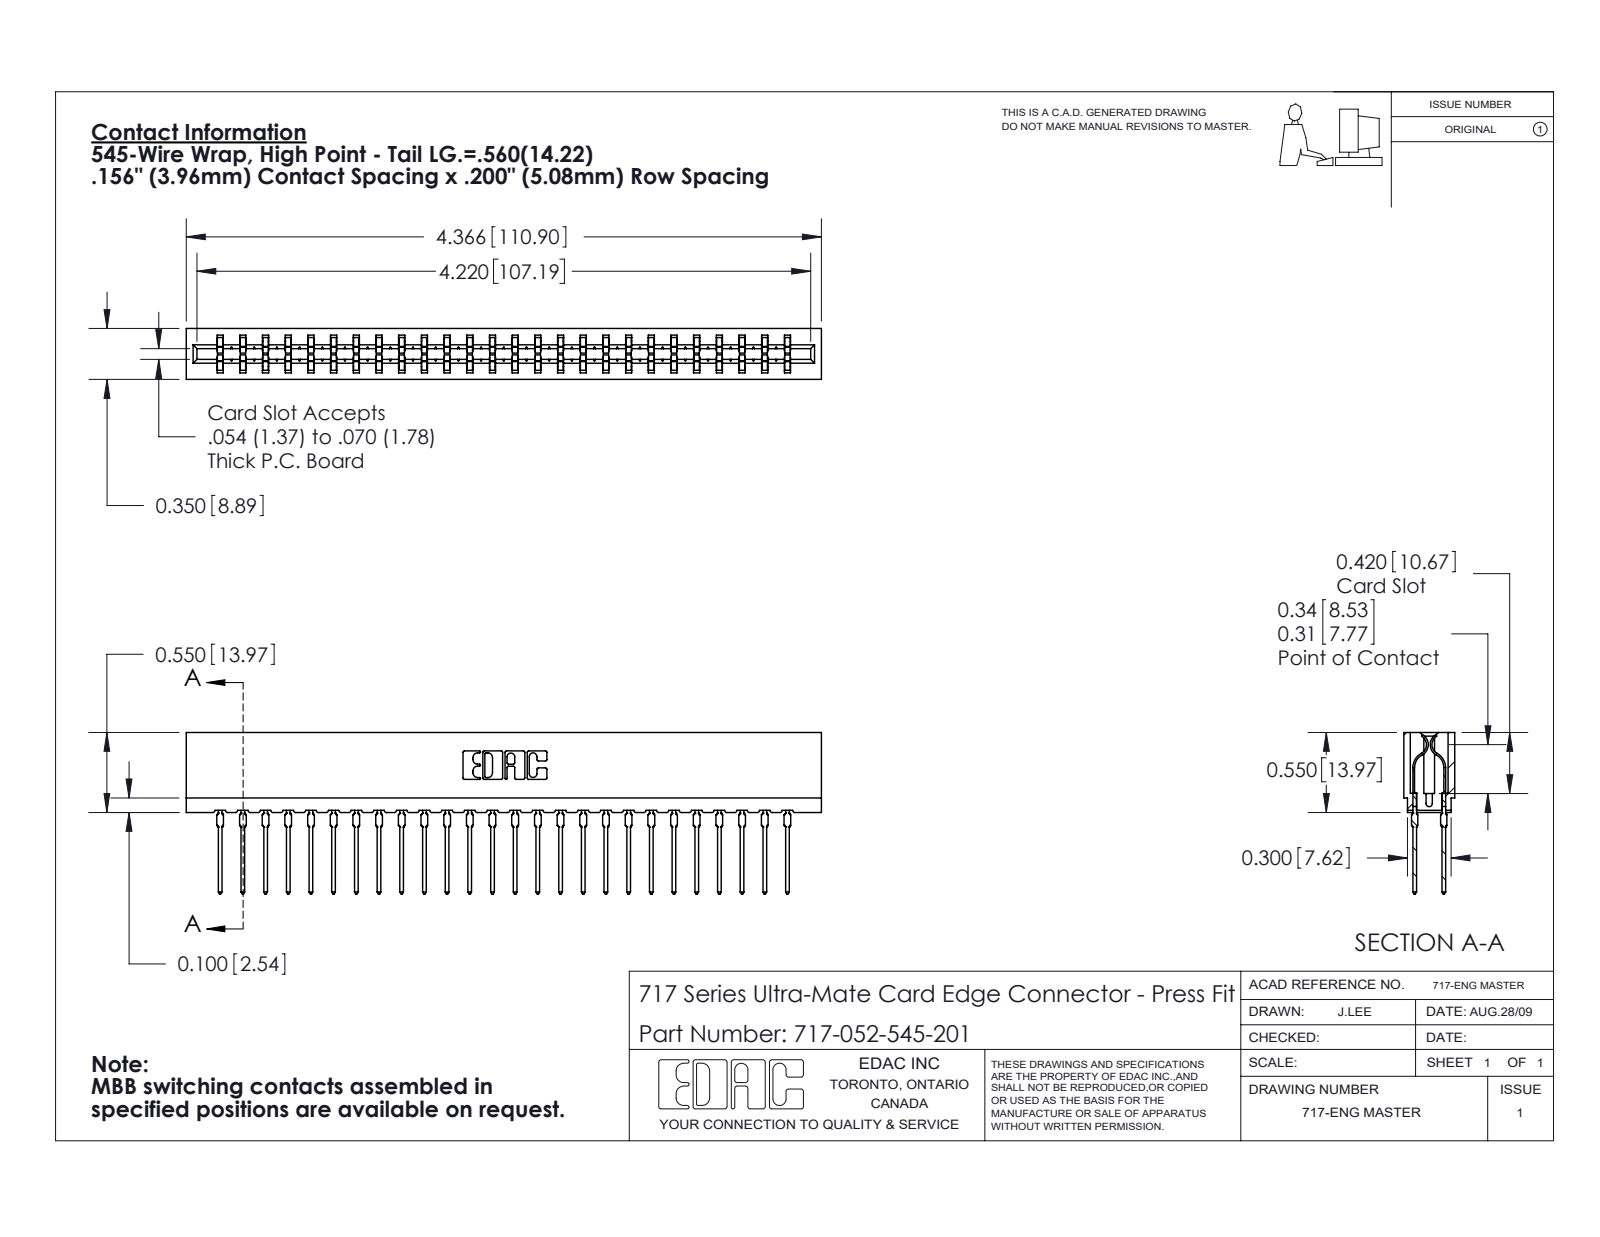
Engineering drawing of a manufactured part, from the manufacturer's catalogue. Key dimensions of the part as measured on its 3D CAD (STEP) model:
Part name (STEP PRODUCT): 717-052-545-201; 745-292-001_545; 717 Part_Insulator Option - 06
STEP written by: SolidWorks 2020 (CONFIG_CONTROL_DESIGN)
Units: inches
Bodies: 53 solids, 4774 faces (2472 planar, 950 cylindrical, 1352 other)
Overall size (bounding box): 4.366 × 1.109 × 0.35
Volume: 0.602 in³ · Surface area: 24.41 in²
Partial cylindrical surfaces — rounded edges, fillets, slot ends (radius × count): R0.021 ×104, R0.015 ×52, R0.01 ×22, R0.005 ×8, R0.011 ×8, R0.007 ×6, R0.031 ×6, R0.026 ×3
Main face-to-face distances: 0.212, 0.138, 0.35, 0.063, 0.287, 0.076, 0.149, 0.156, 0.074, 0.087
